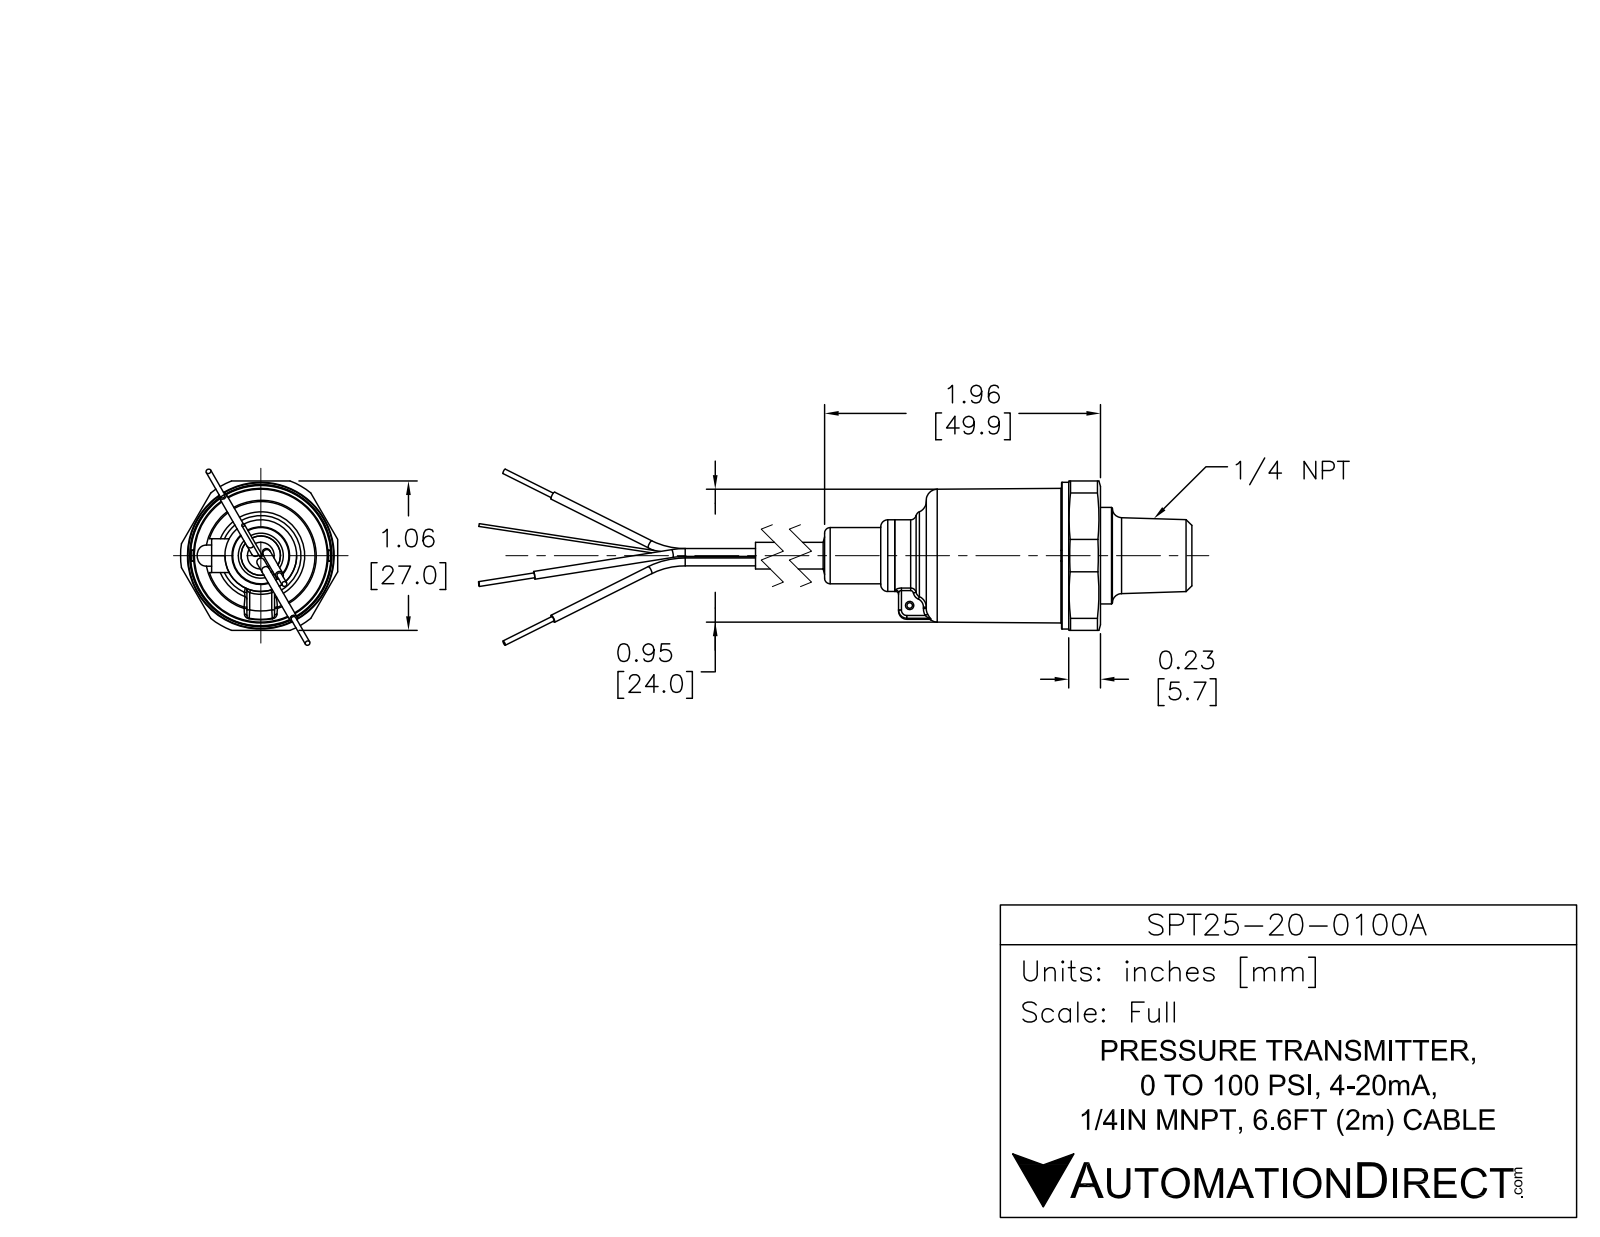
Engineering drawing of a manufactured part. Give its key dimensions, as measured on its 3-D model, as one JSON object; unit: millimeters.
{"part_name": "SPT25-20-0100A", "step_written_by": "SolidWorks 2017 (AUTOMOTIVE_DESIGN)", "units": "millimeters", "bodies": {"solids": 7, "faces": 116, "planar": 32, "cylindrical": 49, "other": 35}, "overall_size": [153.3, 29, 27.09], "volume_mm3": 20801, "surface_area_mm2": 7170, "round_holes": [[1, 1], [3.3, 1]], "round_bosses_or_shafts": [[1.4, 6], [0.75, 5], [26.75, 1], [24, 1], [17.5, 1], [14, 1], [13, 1], [10, 1]], "partial_cylinders_radius": [[2, 1], [14.5, 1]], "face_to_face_distances": [6.75, 24, 17.25, 42.75, 49.5, 66.75, 44, 1.25, 5.5, 22.75]}
